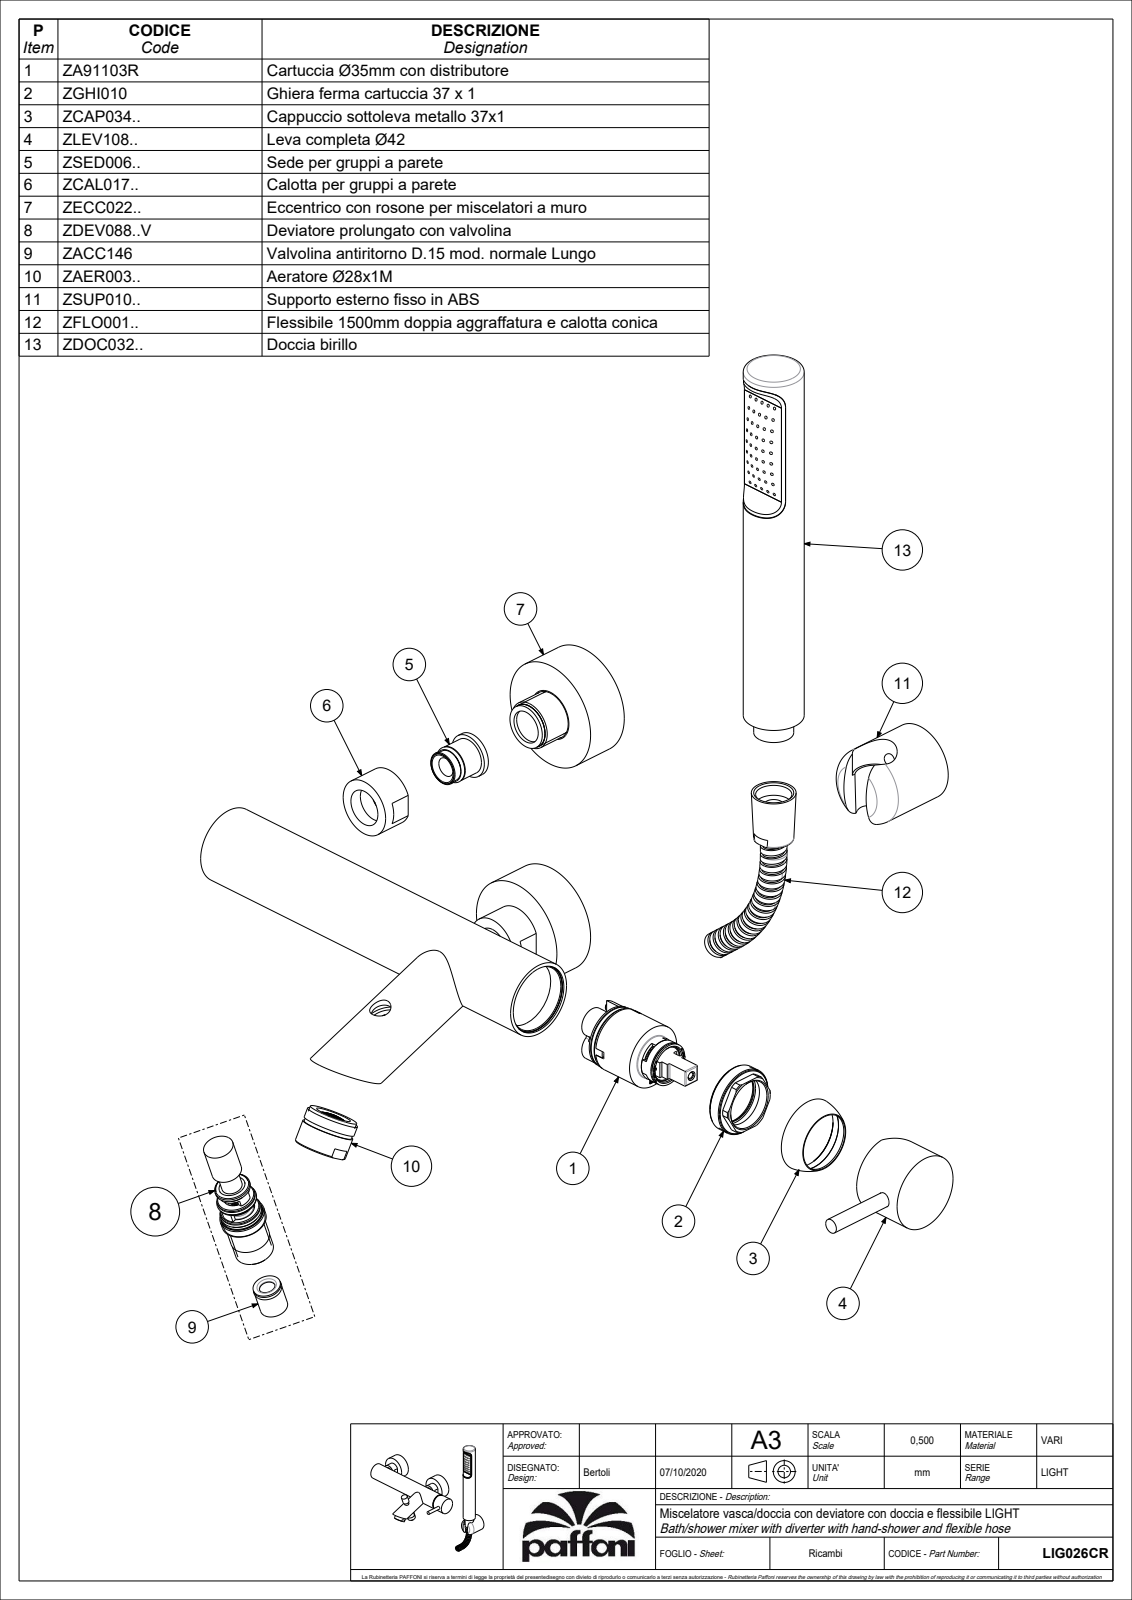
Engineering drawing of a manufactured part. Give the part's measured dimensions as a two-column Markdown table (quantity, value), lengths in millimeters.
| quantity | value |
| --- | --- |
| part name | LIG026CR |
| STEP written by | CREO PARAMETRIC BY PTC INC, 2020044 (CONFIG_CONTROL_DESIGN) |
| units | millimeters |
| bodies | 0 solids, 777 faces (355 planar, 252 cylindrical, 170 other) |
| overall size | 427.94 × 376.31 × 171.48 |
| round holes (diameter × count) | 7.5 × 6, 5 × 5, 8 × 4, 12 × 4, 9 × 3, 24.5 × 3, 1.5 × 2, 10.5 × 2, 14.5 × 2, 16 × 2, 16.7 × 2, 25 × 2 |
| round bosses / shafts (diameter × count) | 12 × 3, 59.7 × 2, 31.5 × 2, 21 × 2, 19.7 × 2, 42 × 1, 41.5 × 1, 35 × 1 |
| partial cylindrical surfaces (radius × count) | 0.5 × 25, 0.3 × 4, 7 × 4, 0.75 × 3, 1 × 2, 4.5 × 2, 7.8 × 2, 7.95 × 2 |
| main face-to-face distances | 5, 25, 20, 23, 10, 18, 13, 43, 0.5, 9.5 |
| hole center spacings | 6.13, 6, 0.71, 1.25, 2.64, 6.16, 8.51, 8.6 |
